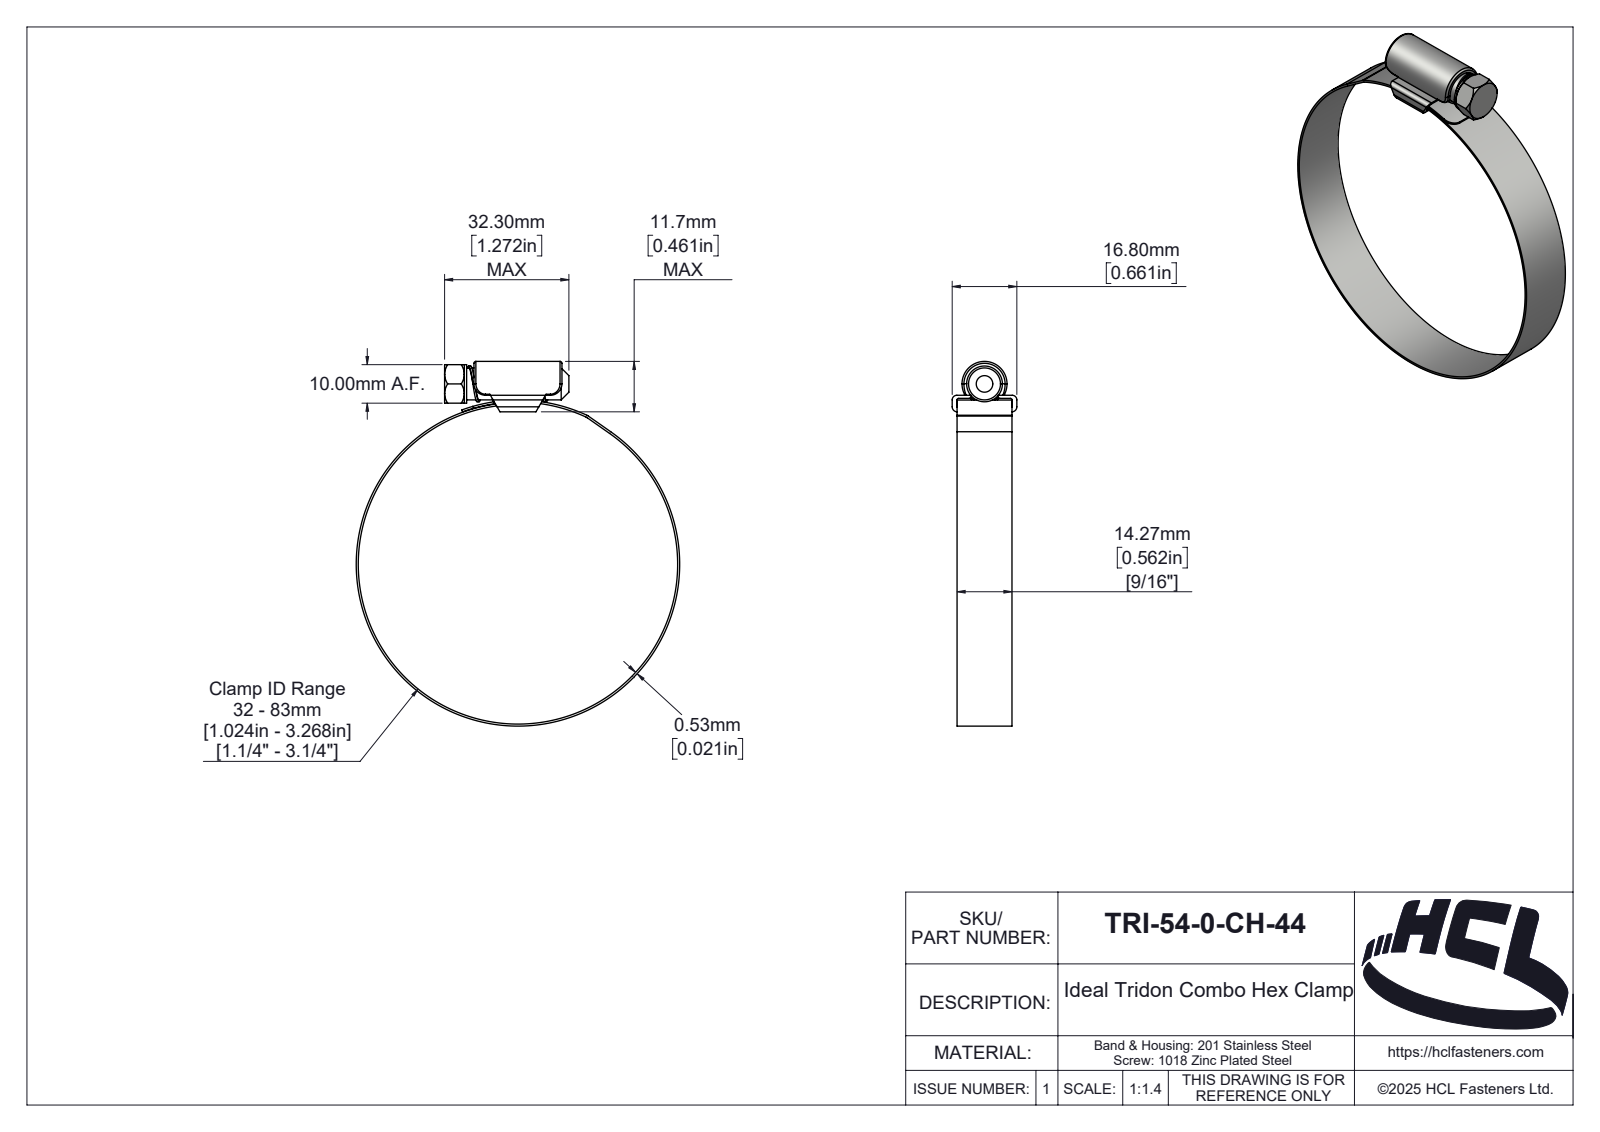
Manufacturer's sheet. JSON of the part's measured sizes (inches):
{"part_name": "TRI-54-0-CH-44", "step_written_by": "SolidWorks 2025 (AUTOMOTIVE_DESIGN)", "units": "inches", "bodies": {"solids": 3, "faces": 212, "planar": 35, "cylindrical": 101, "other": 76}, "overall_size": [3.73, 3.309, 0.661], "volume_in3": 0.304, "surface_area_in2": 17.36, "round_holes": [[3.268, 1]], "round_bosses_or_shafts": [[3.309, 1], [0.394, 1], [0.327, 1]], "partial_cylinders_radius": [[0.02, 6], [0.118, 4], [0.004, 2], [0.047, 2], [0.051, 2], [0.018, 1], [0.074, 1], [0.079, 1]], "face_to_face_distances": [0.047, 0.561, 0.021, 0.138, 0.091, 0.169, 0.122, 0.031, 0.393, 0.05]}
